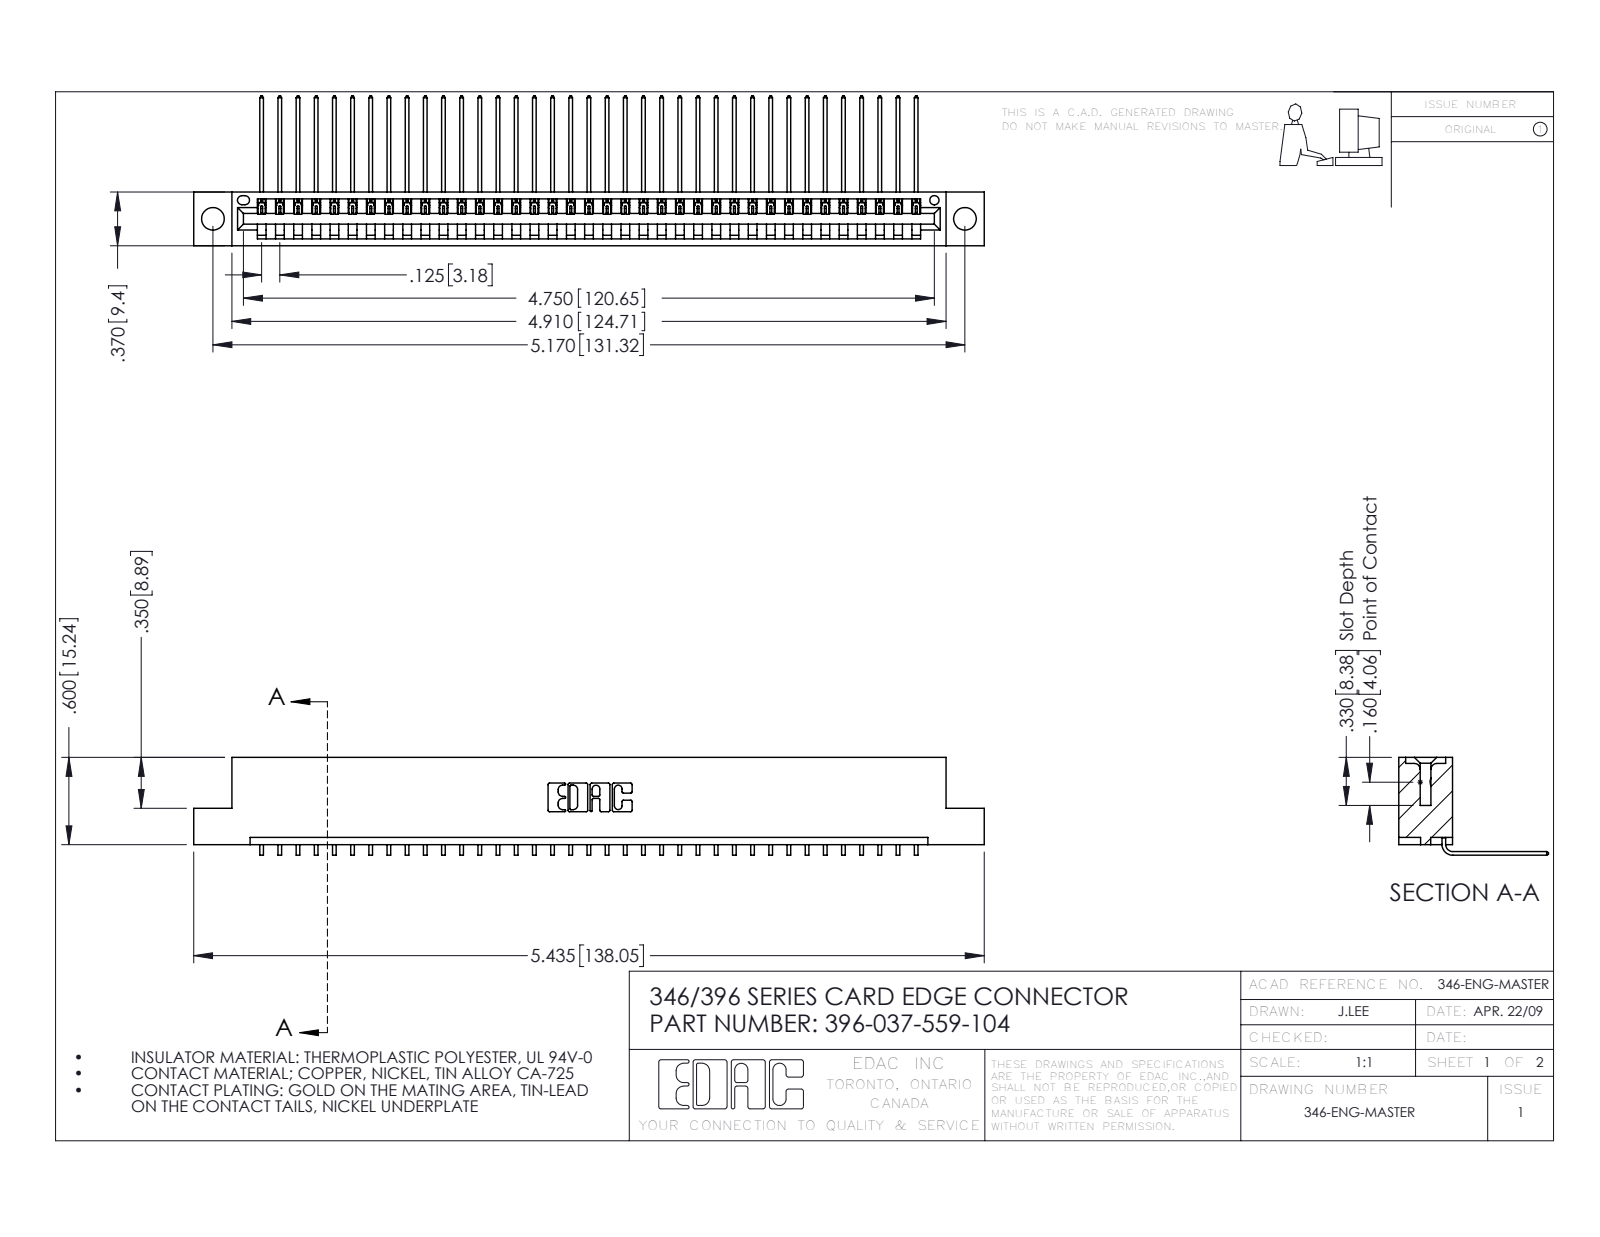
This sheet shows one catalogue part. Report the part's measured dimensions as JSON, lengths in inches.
{"part_name": "346 Part_Flush Mounting Lugs - 0.156 Dia-TH; 396-037-559-104; 345-292-001_558 559 Tail - 1", "step_written_by": "SolidWorks 2016 (CONFIG_CONTROL_DESIGN)", "units": "inches", "bodies": {"solids": 38, "faces": 2342, "planar": 1630, "cylindrical": 712, "other": 0}, "overall_size": [5.435, 1.03, 0.673], "volume_in3": 0.806, "surface_area_in2": 26.36, "round_holes": [[0.156, 2], [0.064, 1]], "partial_cylinders_radius": [[0.006, 74], [0.01, 22], [0.007, 6], [0.031, 6], [0.026, 3], [0.031, 2], [0.04, 2], [0.014, 1]], "face_to_face_distances": [0.048, 0.322, 0.37, 0.25, 0.025, 0.072, 0.298, 0.148, 0.222, 0.1], "hole_center_spacings": [0.246, 4.961, 5.17]}
